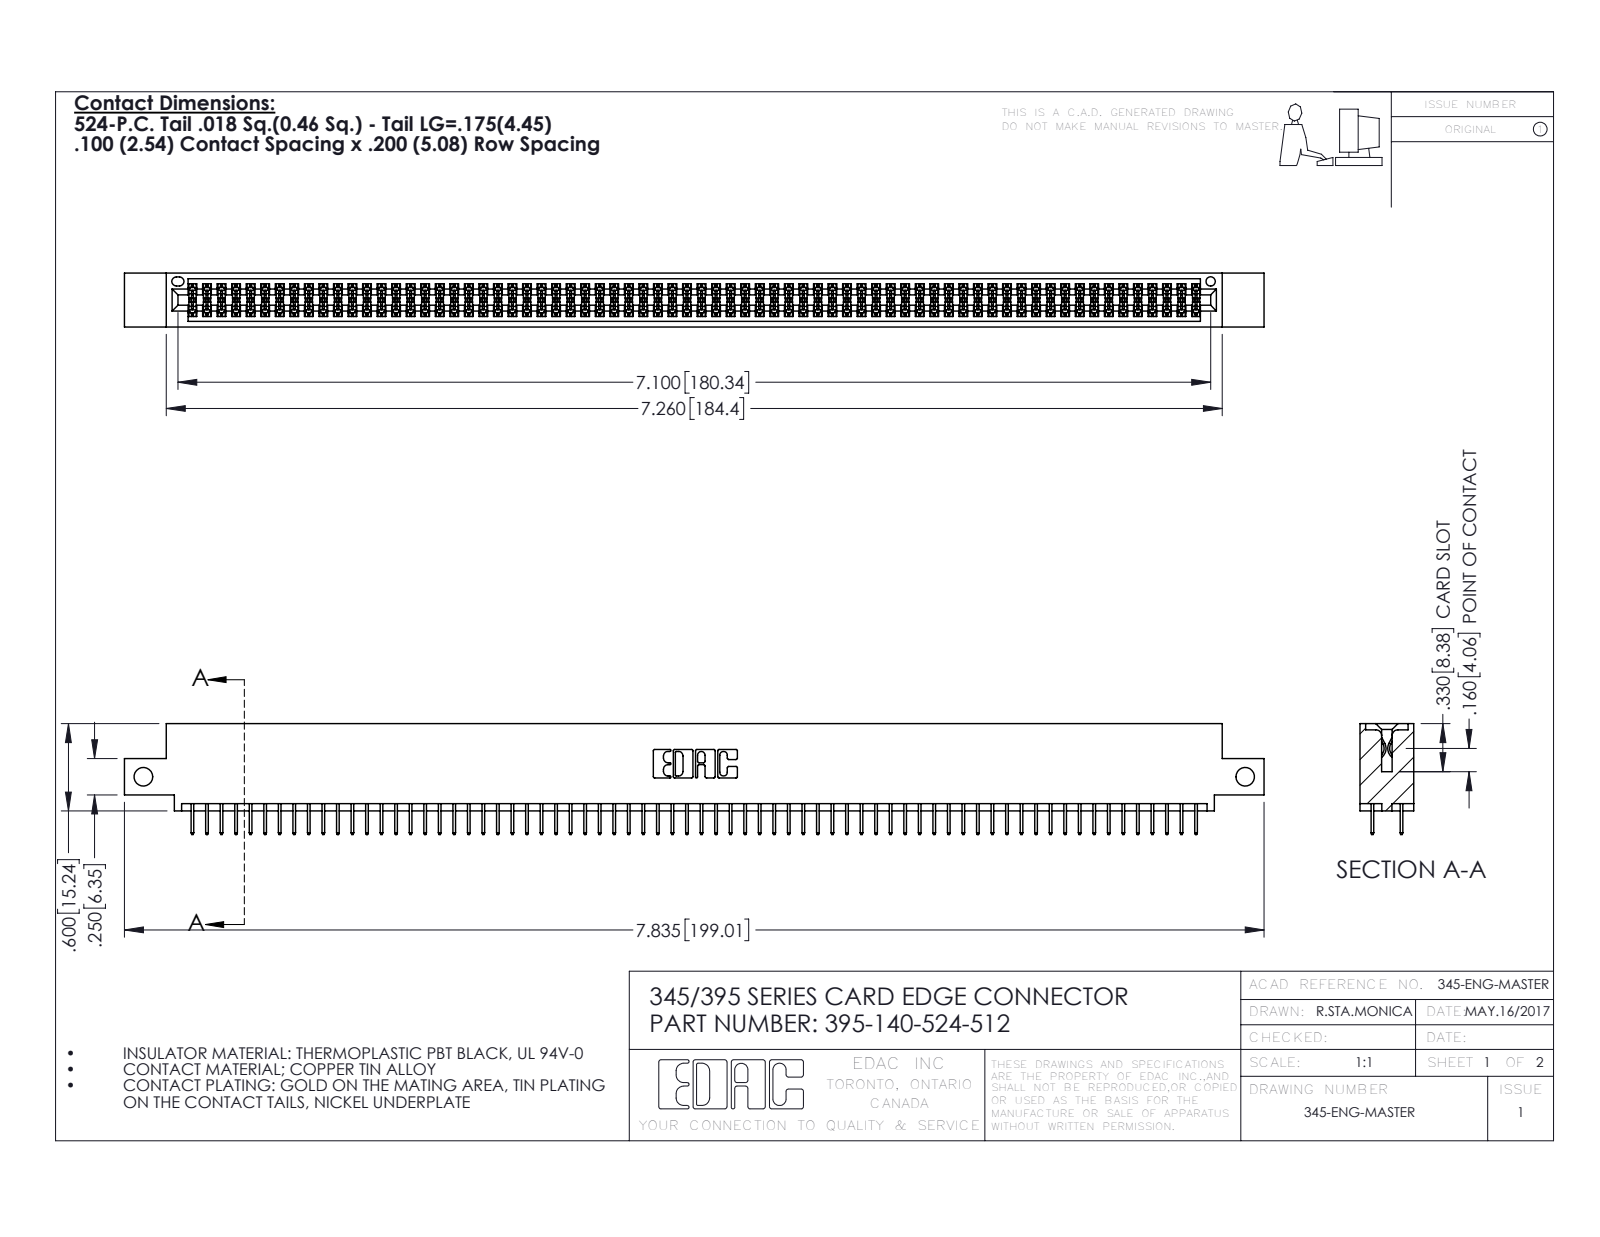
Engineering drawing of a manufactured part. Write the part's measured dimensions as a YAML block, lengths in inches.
part_name: "395-140-524-512; 345-292-001_345-293-124; 345 Part_0.110 Offset - Side Mount"
step_written_by: "SolidWorks 2016 (CONFIG_CONTROL_DESIGN)"
units: inches
bodies: {solids: 141, faces: 7690, planar: 5544, cylindrical: 2146, other: 0}
overall_size: [7.835, 0.762, 0.37]
volume: 1.173
surface_area: 43.94
round_holes:
  - {diameter: 0.128, count: 2}
  - {diameter: 0.064, count: 1}
partial_cylinders:
  - {radius: 0.006, count: 210}
  - {radius: 0.01, count: 22}
  - {radius: 0.007, count: 6}
  - {radius: 0.031, count: 6}
  - {radius: 0.026, count: 3}
  - {radius: 0.014, count: 2}
  - {radius: 0.019, count: 2}
  - {radius: 0.022, count: 2}
face_to_face_distances: [0.072, 0.298, 0.2, 0.37, 0.098, 0.272, 0.025, 0.225, 0.072, 0.175]
hole_center_spacings: [7.575]
